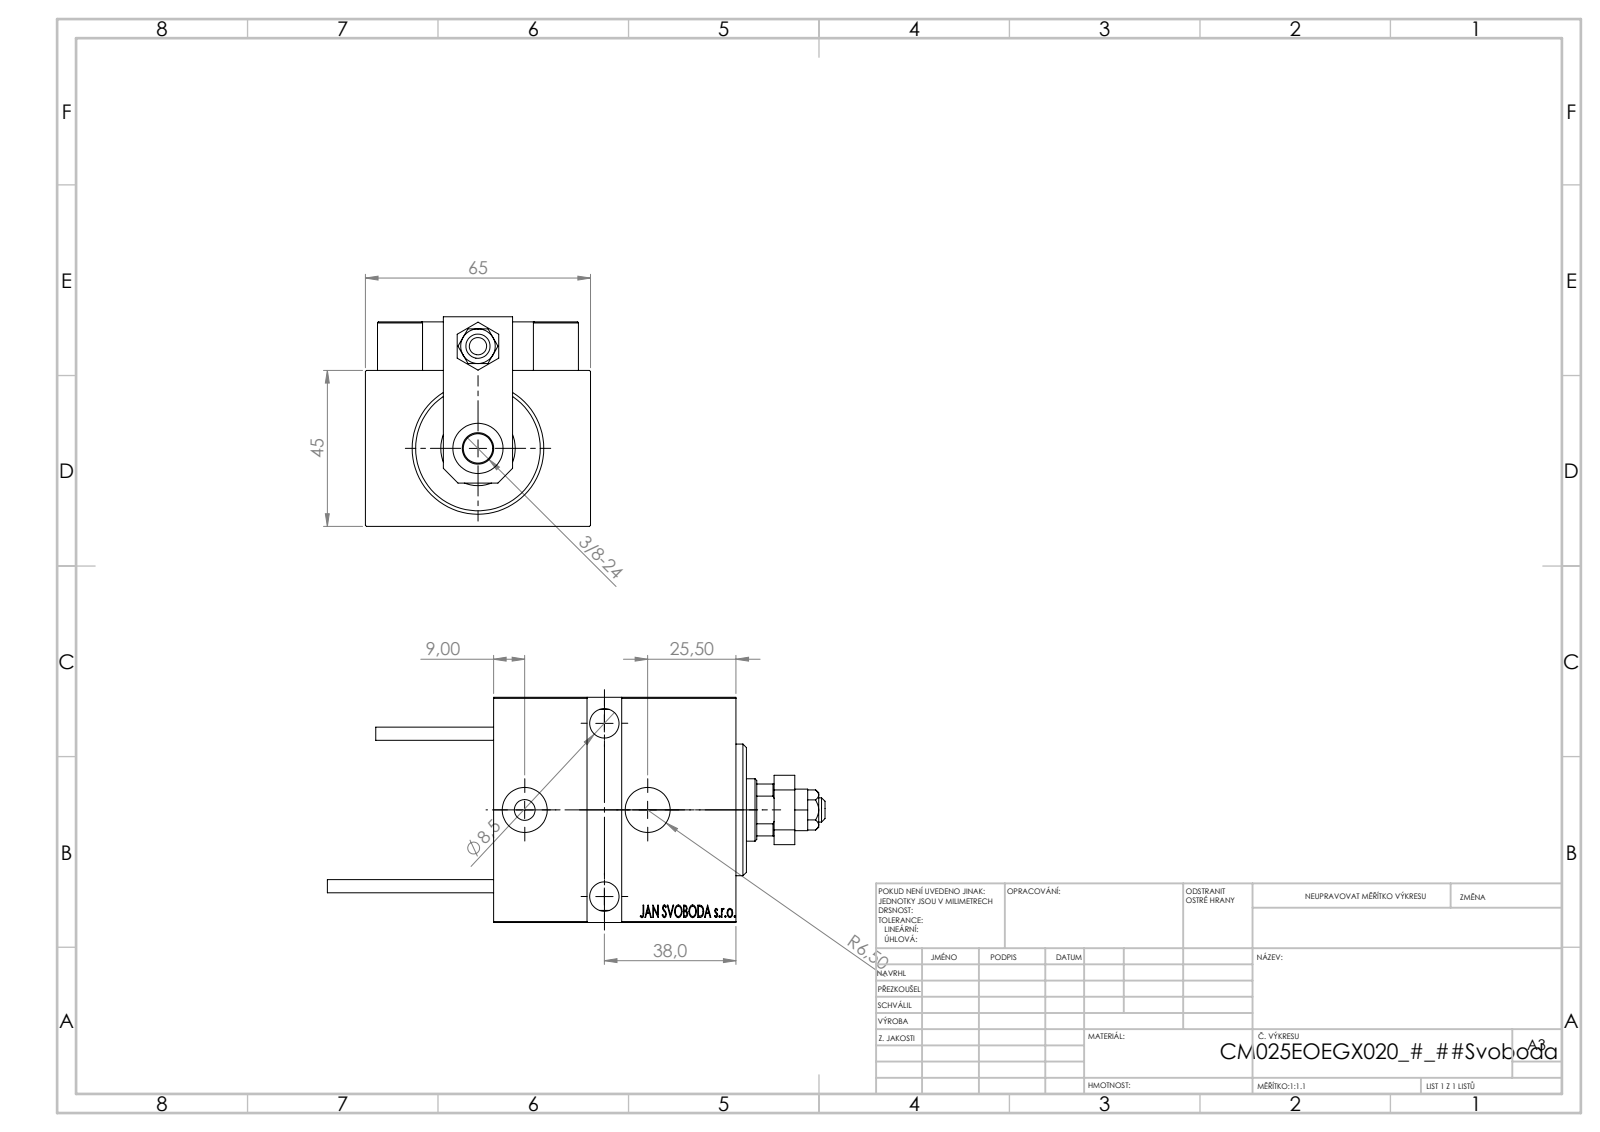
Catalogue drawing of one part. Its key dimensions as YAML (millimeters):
part_name: "ALLEN BOLT D8; V450CM_E_Body; NUT_D12; Block (+7 more)"
step_written_by: "SolidWorks 2019 (CONFIG_CONTROL_DESIGN)"
units: millimeters
bodies: {solids: 24, faces: 1276, planar: 567, cylindrical: 168, other: 541}
overall_size: [143.7, 65, 60.5]
volume: 240199
surface_area: 62347
round_holes:
  - {diameter: 8, count: 5}
  - {diameter: 3.2, count: 4}
  - {diameter: 4, count: 4}
  - {diameter: 8.5, count: 3}
  - {diameter: 5, count: 2}
  - {diameter: 13, count: 2}
  - {diameter: 13.5, count: 2}
  - {diameter: 7, count: 1}
  - {diameter: 14.5, count: 1}
  - {diameter: 18, count: 1}
  - {diameter: 21.5, count: 1}
  - {diameter: 25, count: 1}
round_bosses_or_shafts:
  - {diameter: 5, count: 2}
  - {diameter: 3.8, count: 2}
  - {diameter: 38, count: 1}
  - {diameter: 27, count: 1}
  - {diameter: 13, count: 1}
  - {diameter: 11, count: 1}
  - {diameter: 6, count: 1}
partial_cylinders:
  - {radius: 0.3, count: 30}
  - {radius: 3, count: 2}
  - {radius: 8.5, count: 1}
face_to_face_distances: [45, 65, 14, 59, 6, 19, 8, 70, 58, 13]
hole_center_spacings: [10.77, 11.37, 20, 21.03, 22.09, 27.95, 29.59, 29.69]
